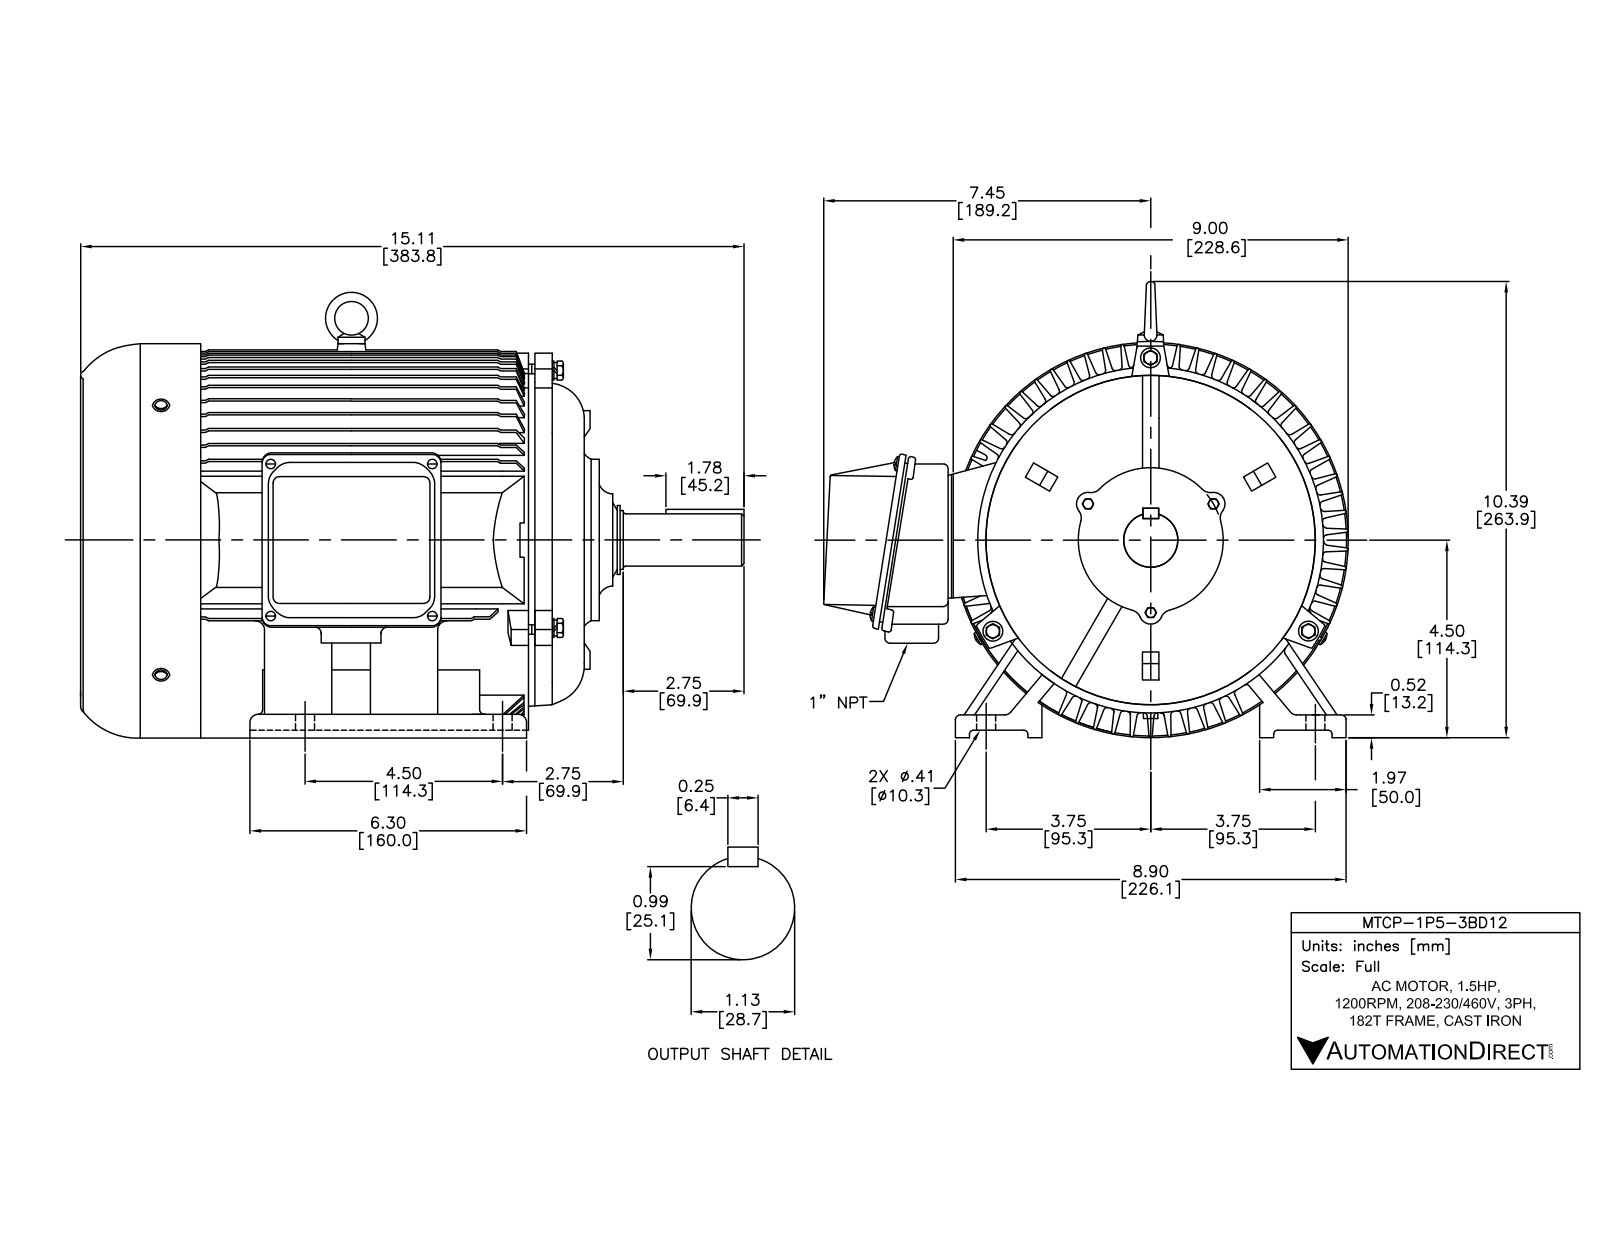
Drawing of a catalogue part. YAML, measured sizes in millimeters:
part_name: "hex head bolts-full thread grade c gb_GB_FASTENER_BOLT_HHBFTC M6X35-N; PE140接线盒座_默认_按加工; plain washers-n series-grade a gb_GB_FASTENER_WASHER_PWNA 6; spring lock washers--normal type gb_GB_FASTENER_WASHER_SW 6 (+6 more)"
step_written_by: "SolidWorks 2017 (AUTOMOTIVE_DESIGN)"
units: millimeters
bodies: {solids: 47, faces: 2451, planar: 722, cylindrical: 968, other: 761}
overall_size: [382.55, 246.78, 182.39]
volume: 1864000
surface_area: 745641
round_holes:
  - {diameter: 5.8, count: 14}
  - {diameter: 9, count: 12}
  - {diameter: 4.2, count: 11}
  - {diameter: 5, count: 3}
  - {diameter: 5.3, count: 3}
  - {diameter: 5.4, count: 3}
  - {diameter: 6.4, count: 3}
  - {diameter: 6.68, count: 3}
  - {diameter: 7, count: 3}
  - {diameter: 7.69, count: 3}
  - {diameter: 2, count: 2}
  - {diameter: 8, count: 1}
round_bosses_or_shafts:
  - {diameter: 5, count: 11}
  - {diameter: 12, count: 3}
  - {diameter: 10, count: 3}
  - {diameter: 9.88, count: 3}
  - {diameter: 8, count: 3}
  - {diameter: 6, count: 3}
  - {diameter: 175.4, count: 1}
  - {diameter: 173, count: 1}
partial_cylinders:
  - {radius: 0.5, count: 145}
  - {radius: 1, count: 85}
  - {radius: 2, count: 60}
  - {radius: 1.25, count: 27}
  - {radius: 7, count: 21}
  - {radius: 1.2, count: 20}
  - {radius: 0.34, count: 16}
  - {radius: 3, count: 15}
face_to_face_distances: [4, 6, 2, 3, 12, 1.2, 249, 252, 65.05, 63.85]
hole_center_spacings: [54, 139.7, 90, 25.4, 35, 60.4, 76.2, 76.37]
